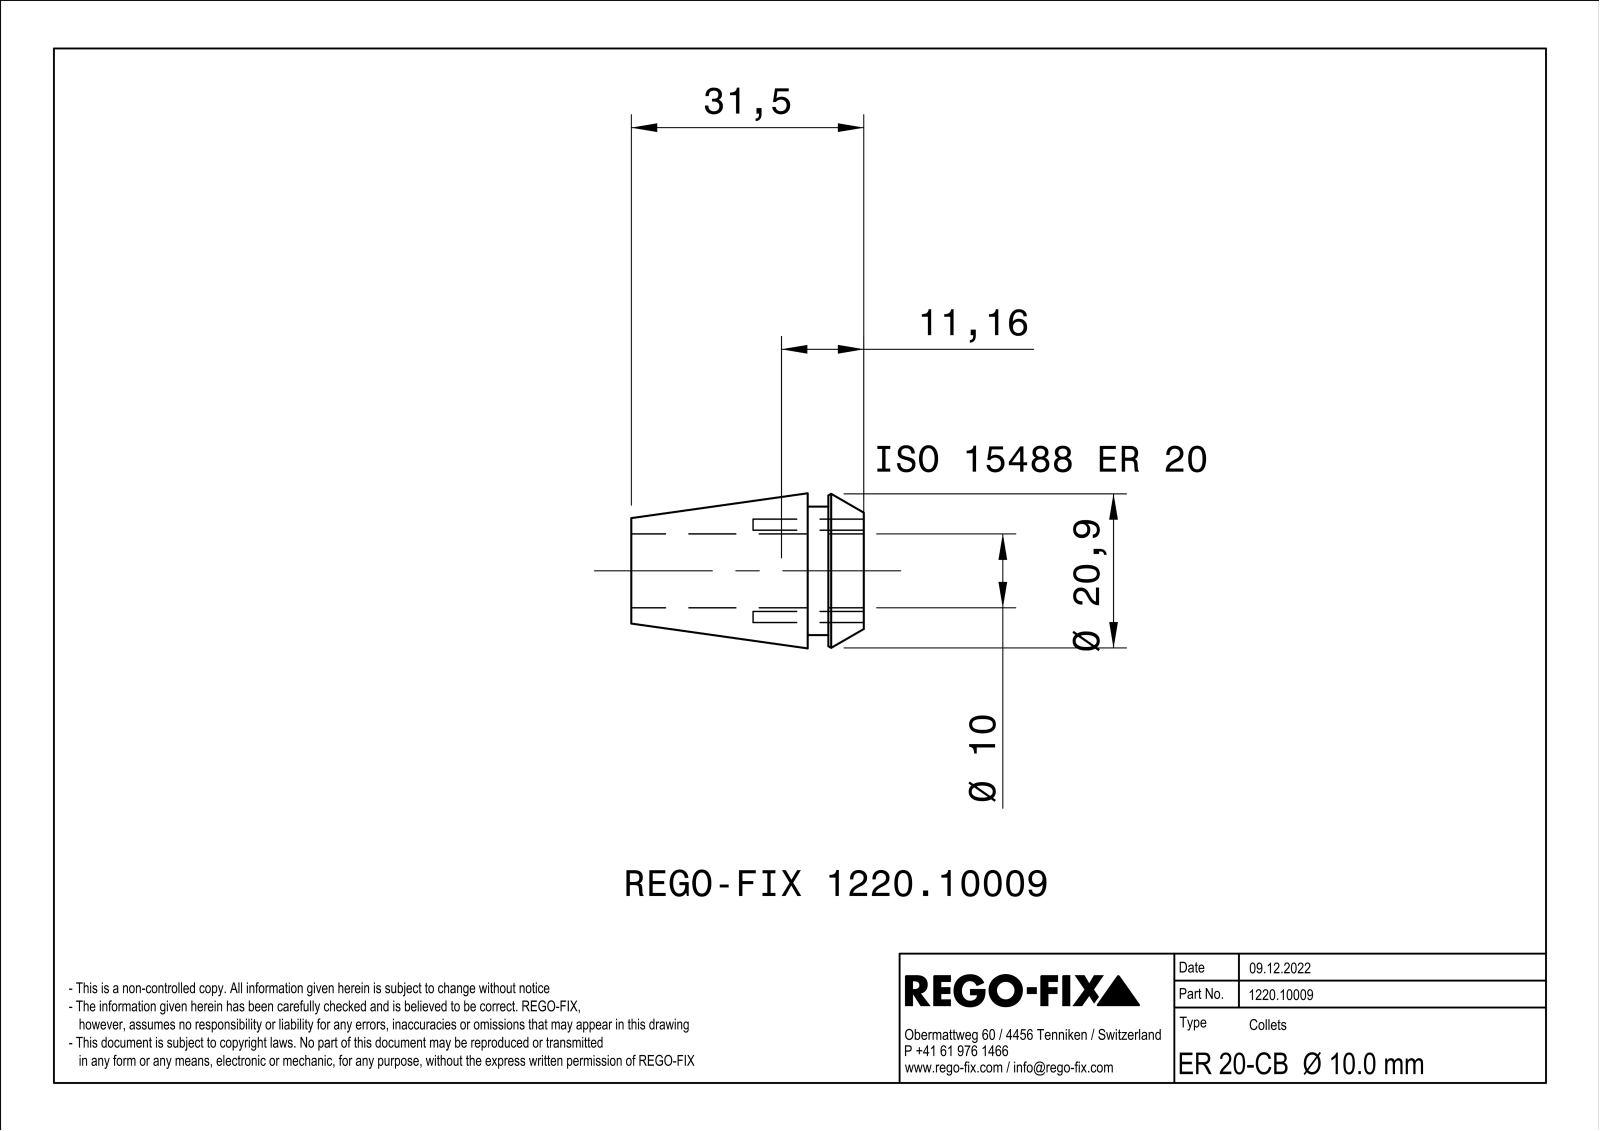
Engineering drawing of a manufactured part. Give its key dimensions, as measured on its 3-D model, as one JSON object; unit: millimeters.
{"part_name": "NOCUT", "step_written_by": "SIEMENS PLM Software Solid Edge ST10 (AUTOMOTIVE_DESIGN)", "units": "millimeters", "bodies": {"solids": 1, "faces": 178, "planar": 64, "cylindrical": 21, "other": 93}, "overall_size": [31.5, 20.99, 20.99], "volume_mm3": 4478, "surface_area_mm2": 5701, "round_holes": [[1.5, 4], [10, 1]], "round_bosses_or_shafts": [[21, 1], [17.4, 1]], "face_to_face_distances": [0.6, 4.8, 7.6, 2.8, 31.5, 26.7, 23.9], "hole_center_spacings": [6.25, 8.83, 12.49]}
